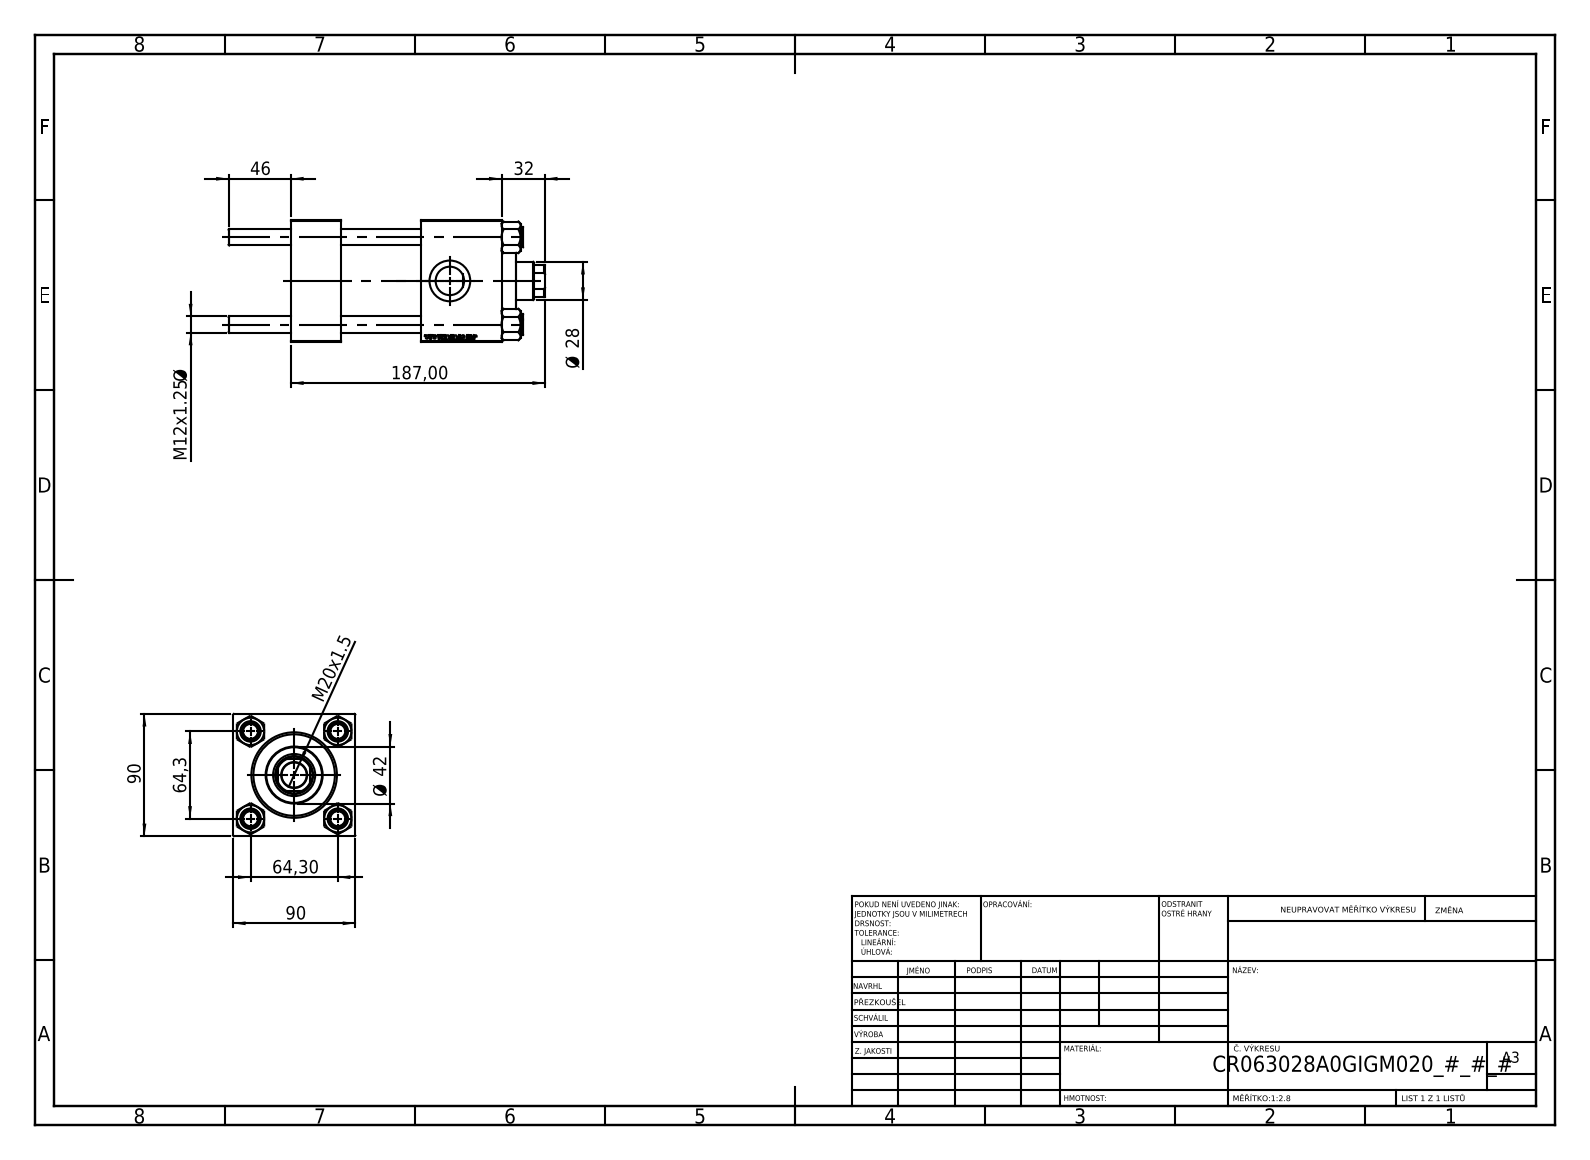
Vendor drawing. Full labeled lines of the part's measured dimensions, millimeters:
Part name (STEP PRODUCT): CR025_012_A_0_G_A_G_M_020_+#_##_TYCINKA; NUT_M5; V215CR_BODY_A; V215_VC_A (+1 more)
STEP written by: SolidWorks 2019 (CONFIG_CONTROL_DESIGN)
Units: millimetres
Bodies: 11 solids, 1133 faces (519 planar, 78 cylindrical, 536 other)
Overall size (bounding box): 233 × 90 × 90
Volume: 980 347 mm³ · Surface area: 195 605 mm²
Round holes (diameter × count): ⌀12 ×4, ⌀7 ×2, ⌀20.96 ×2, ⌀30 ×2, ⌀18.5 ×1, ⌀28 ×1, ⌀31 ×1, ⌀50 ×1, ⌀60 ×1, ⌀63 ×1
Round bosses / shafts (diameter × count): ⌀15 ×4, ⌀69 ×1, ⌀42 ×1
Partial cylindrical surfaces — rounded edges, fillets, slot ends (radius × count): R13.5 ×1
Main face-to-face distances: 90, 59, 37, 155, 118, 96, 126.3, 89.3, 30.3, 28.7
Hole centre spacings: 45.47, 64.3, 90.93
